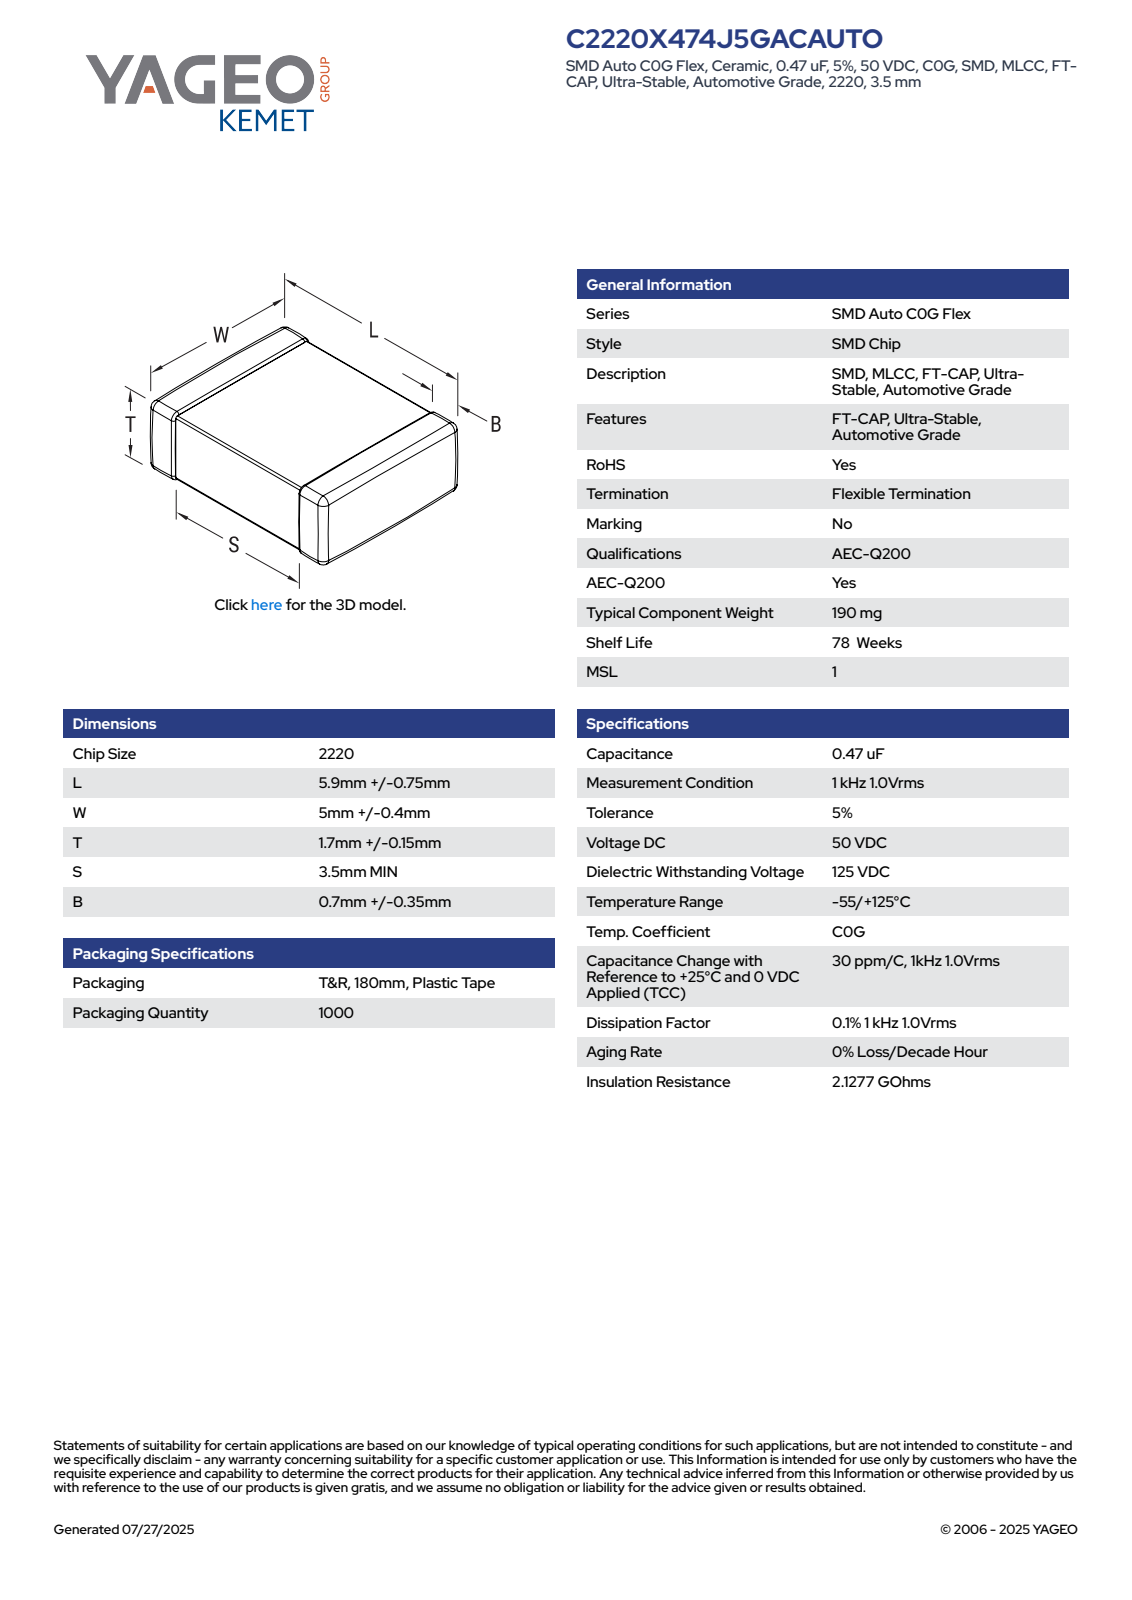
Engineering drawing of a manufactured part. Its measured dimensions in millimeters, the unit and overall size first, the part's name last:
Units: millimetres
Overall size (bounding box): 6.65 × 5.4 × 1.85
Partial cylindrical surfaces — rounded edges, fillets, slot ends (radius × count): R0.11 ×24
Main face-to-face distances: 1.63, 1.74, 1.85, 6.65, 5.18, 5.29, 5.4, 2.8, 3.85, 3.59
Volume: 59 mm³ · Surface area: 115 mm²
Bodies: 4 solids, 121 faces (71 planar, 34 cylindrical, 16 other)
Part name (STEP PRODUCT): CCS_CCSTD_2220_L6.65W5.4T1.85B0.7
STEP written by: SolidWorks 2021 (AUTOMOTIVE_DESIGN)
